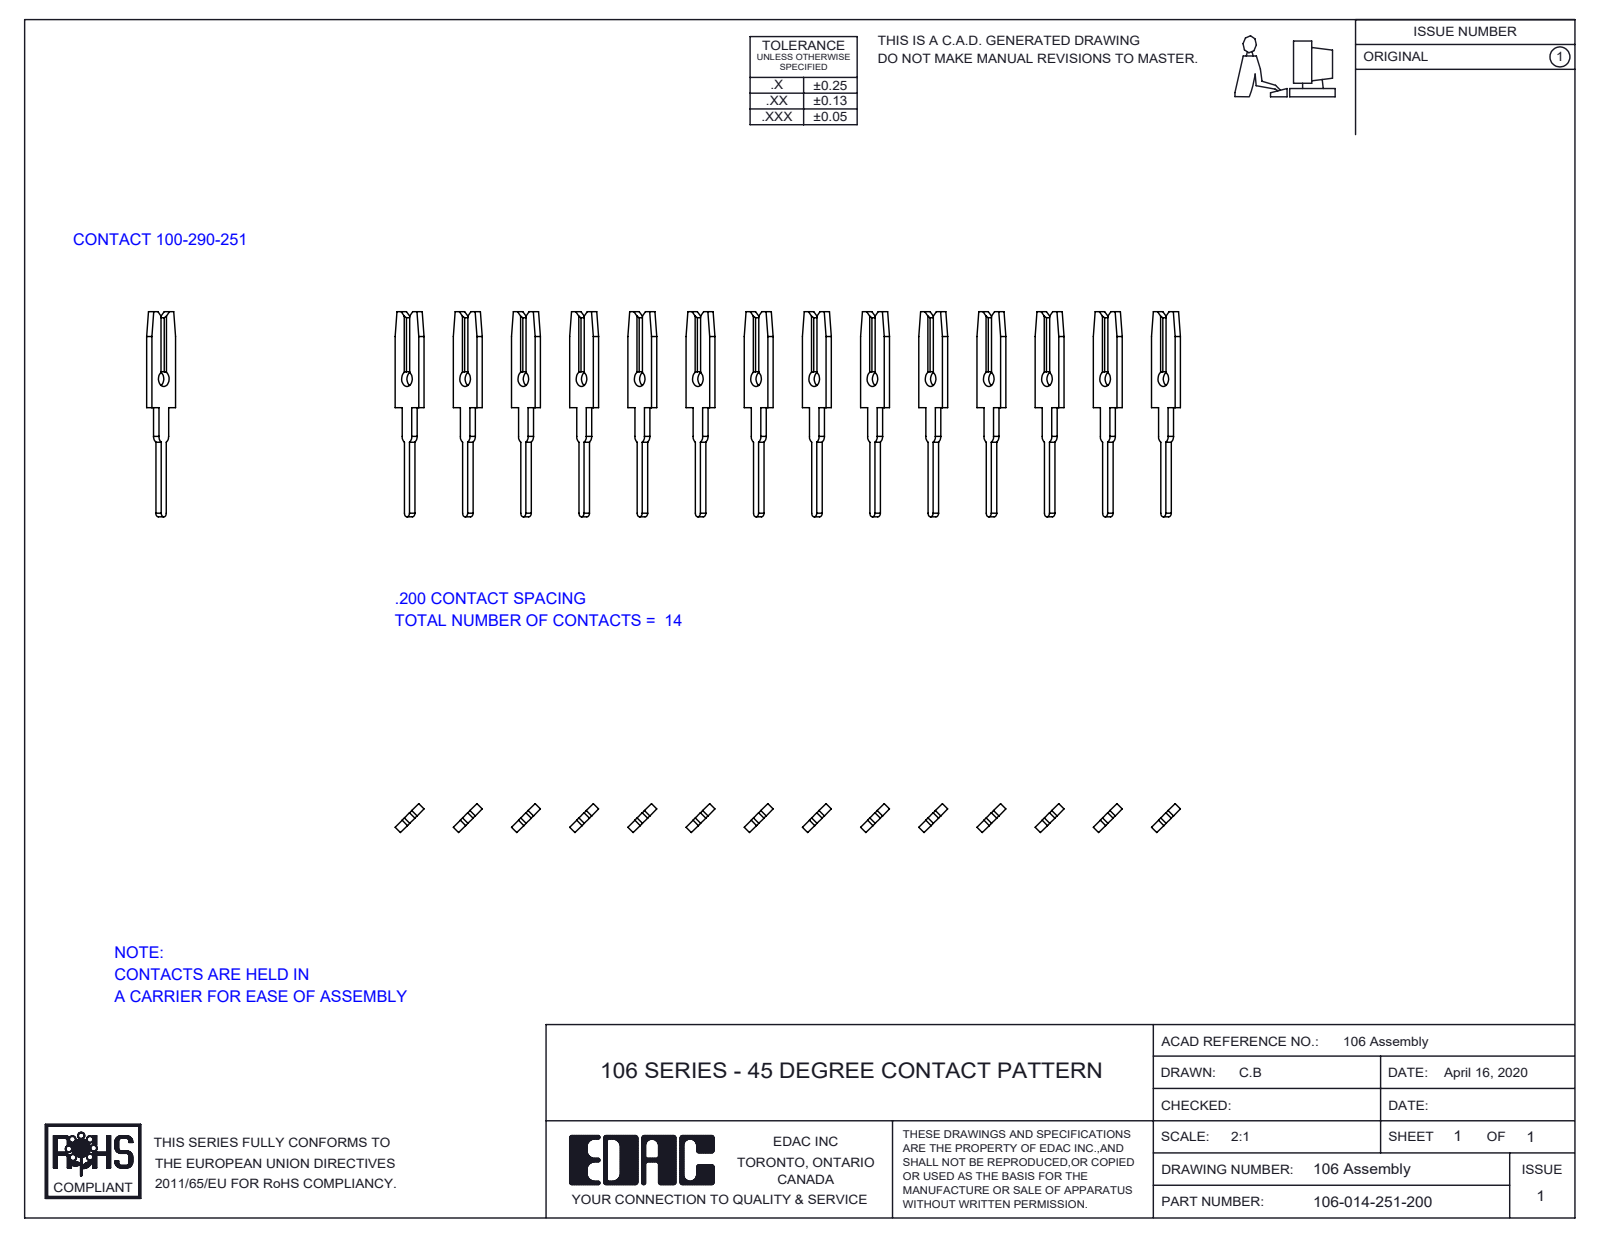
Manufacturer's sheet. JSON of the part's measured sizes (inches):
{"part_name": "100-290-001_100-290-251; 106-014-251-200", "step_written_by": "SolidWorks 2016 (CONFIG_CONTROL_DESIGN)", "units": "inches", "bodies": {"solids": 14, "faces": 392, "planar": 308, "cylindrical": 84, "other": 0}, "overall_size": [2.7, 0.705, 0.1], "volume_in3": 0.016, "surface_area_in2": 1.95, "round_holes": [[0.052, 14]], "partial_cylinders_radius": [[0.012, 14], [0.024, 14]], "face_to_face_distances": [0.141, 0.283, 0.707, 0.566, 0.848, 0.424, 0.424, 0.99, 0.026, 0.874], "hole_center_spacings": [0.141, 0.283, 0.424, 0.566, 0.848, 0.707, 0.99, 1.131]}
